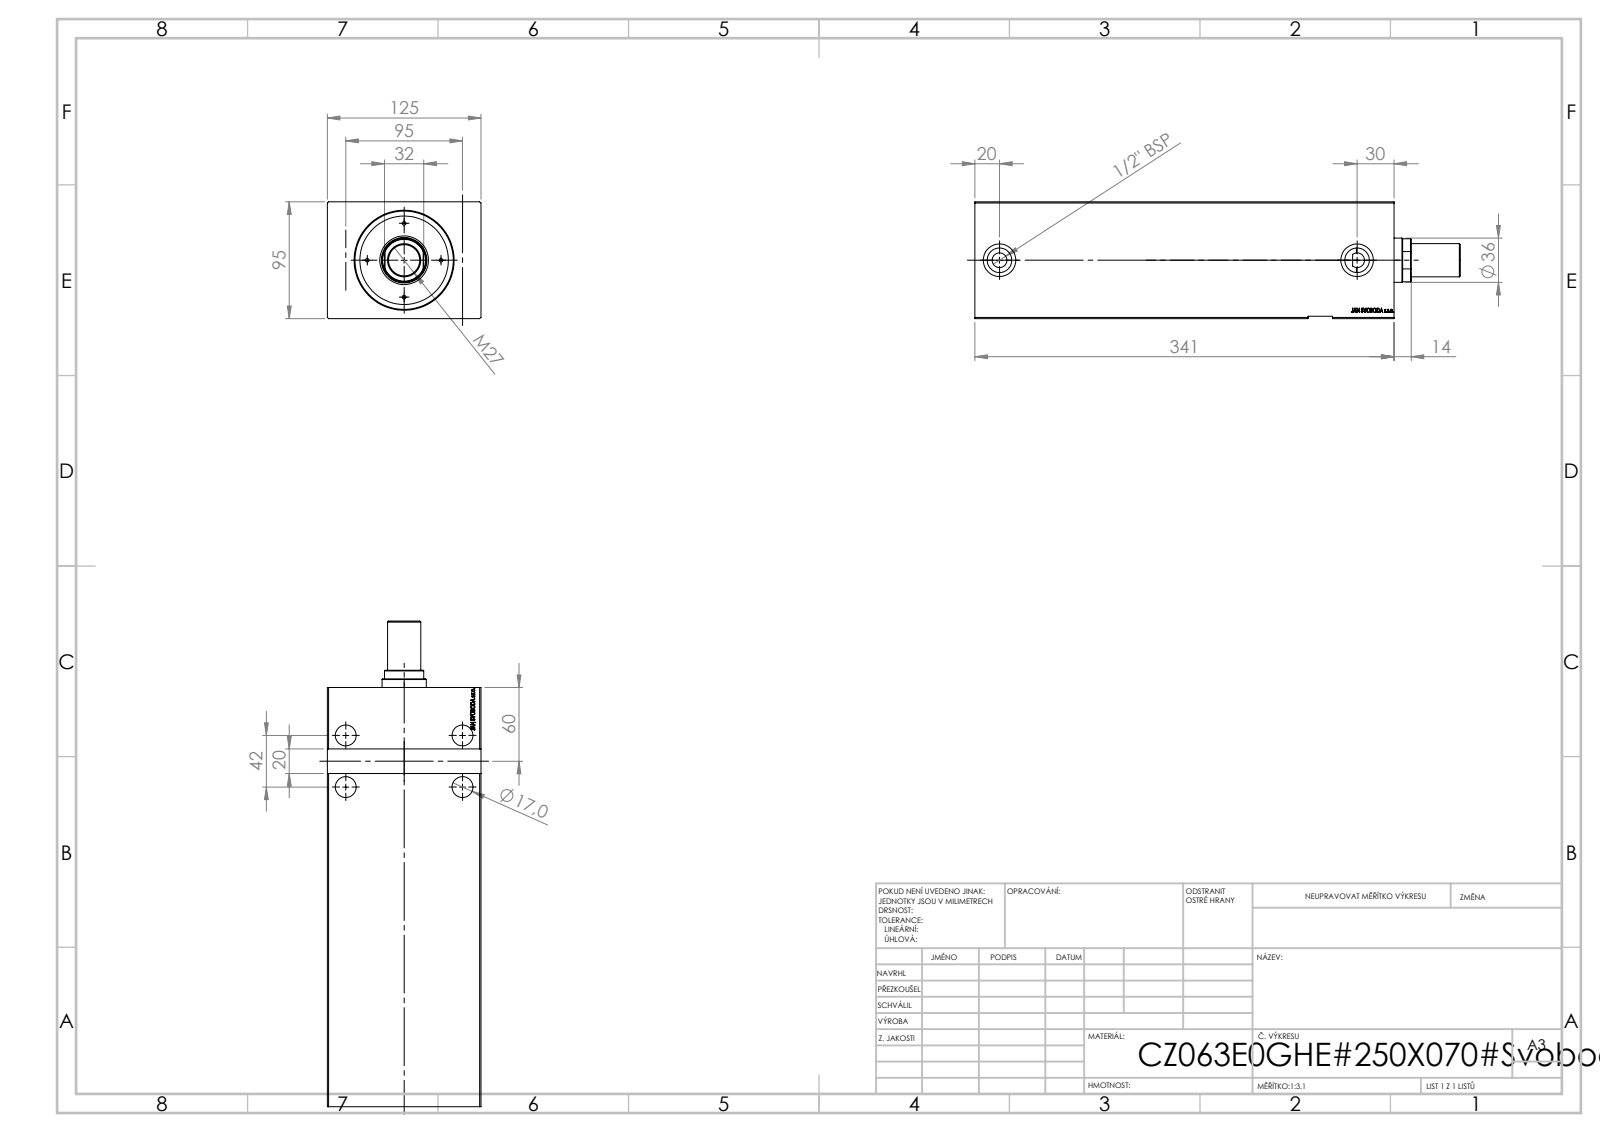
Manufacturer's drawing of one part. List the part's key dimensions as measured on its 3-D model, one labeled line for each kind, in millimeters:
STEP written by: SolidWorks 2019 (CONFIG_CONTROL_DESIGN)
Units: millimetres
Bodies: 1 solid, 805 faces (393 planar, 30 cylindrical, 382 other)
Overall size (bounding box): 341 × 125 × 95
Volume: 2 923 000 mm³ · Surface area: 257 688 mm²
Round holes (diameter × count): ⌀17 ×4, ⌀8 ×2, ⌀20 ×2, ⌀26.5 ×2, ⌀12 ×1, ⌀36 ×1, ⌀63 ×1, ⌀80 ×1
Partial cylindrical surfaces — rounded edges, fillets, slot ends (radius × count): R6 ×1
Main face-to-face distances: 95, 125, 341, 320.2, 20.8, 2, 93, 14, 306.2, 327
Hole centre spacings: 42, 95, 103.87, 27.02, 49.09, 68.01, 79.4, 231.58
